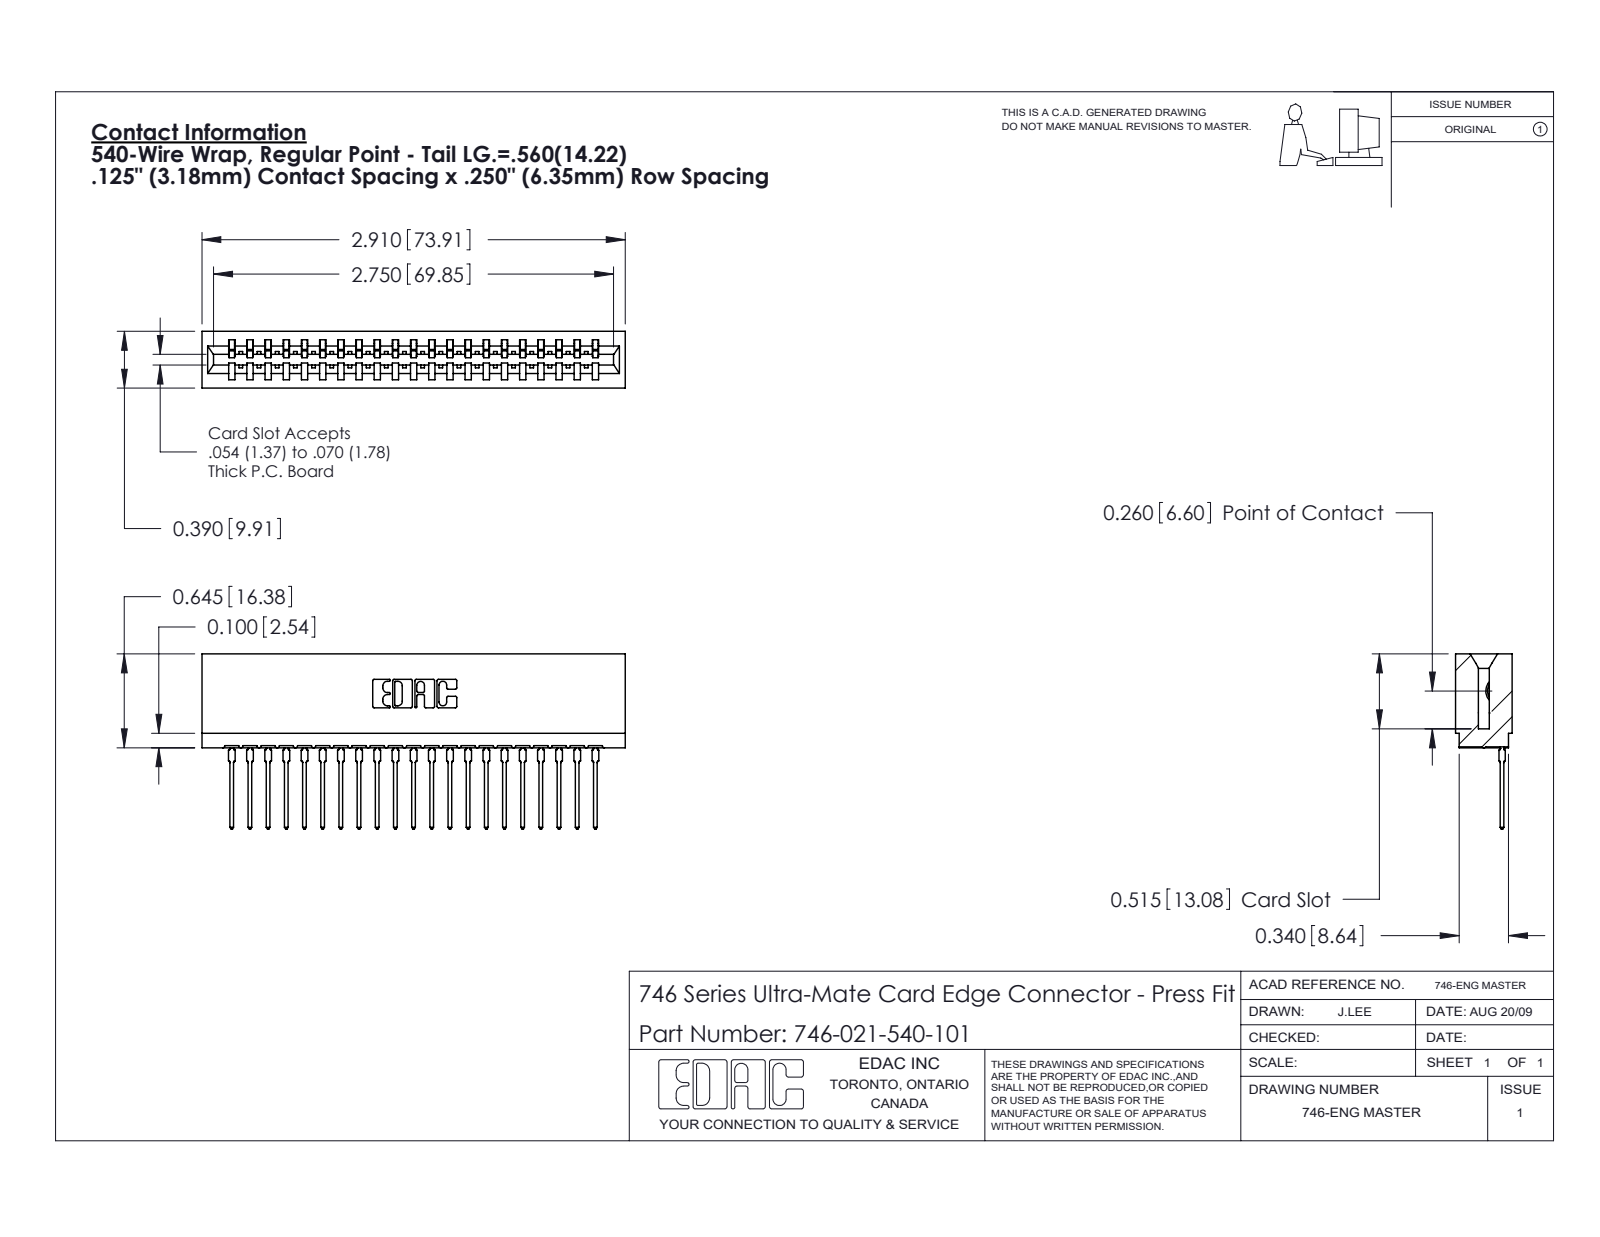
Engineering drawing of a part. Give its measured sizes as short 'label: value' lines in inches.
name: 746-292-001_540; 746 Part_.515 Slot Depth - 01; 746-021-540-101
written by: SolidWorks 2020 (CONFIG_CONTROL_DESIGN)
unit: in
bodies: 22 solids, 2365 faces (1378 planar, 441 cylindrical, 546 other)
size: 2.91 × 1.204 × 0.39
volume: 0.483 in³; area: 18.03 in²
rounds: 42× R0.021, 22× R0.01, 22× R0.015, 6× R0.007, 6× R0.031, 4× R0.005, 4× R0.011, 3× R0.026
face distances: 0.25, 0.333, 0.057, 0.39, 0.5, 0.025, 0.307, 0.042, 0.125, 0.083
